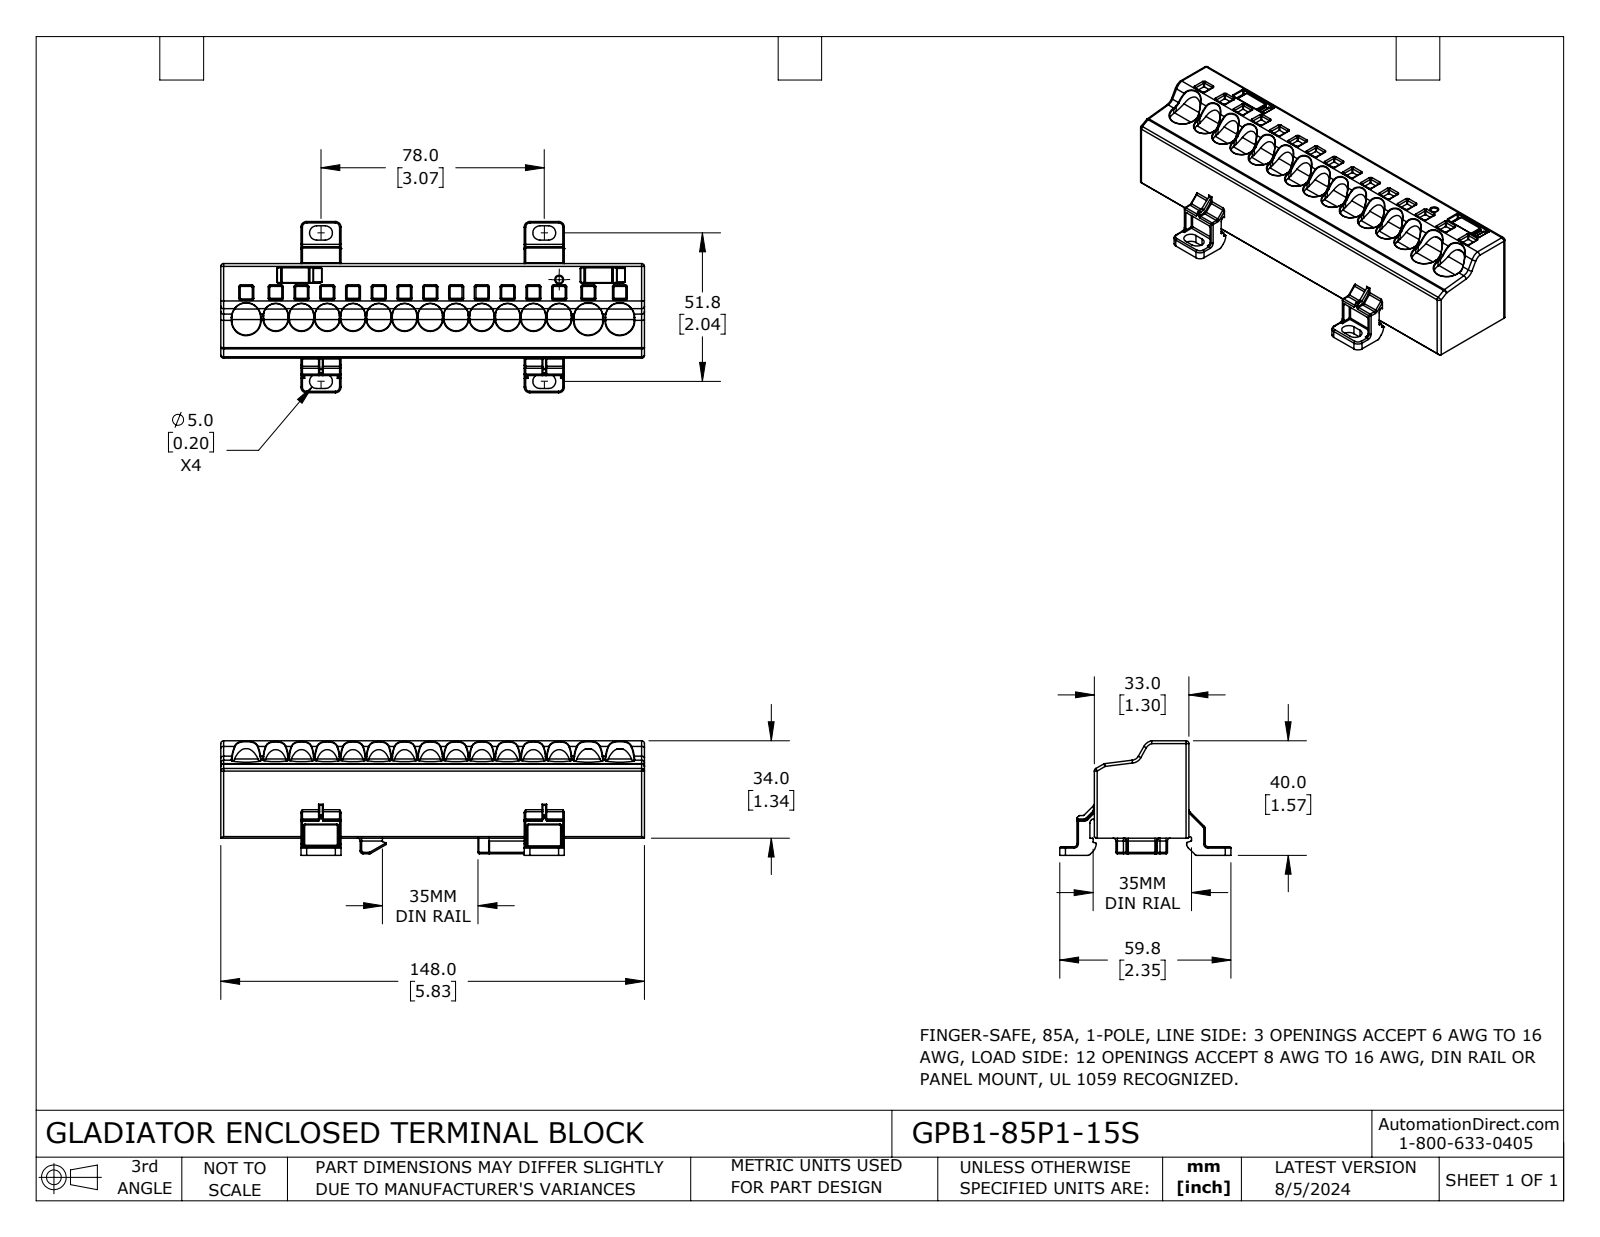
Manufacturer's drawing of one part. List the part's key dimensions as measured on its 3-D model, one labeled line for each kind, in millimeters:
Part name (STEP PRODUCT): GPB1-85P1-15S
STEP written by: SolidWorks 2023 (CONFIG_CONTROL_DESIGN)
Units: millimetres
Bodies: 1 solid, 1038 faces (292 planar, 426 cylindrical, 320 other)
Overall size (bounding box): 148 × 59.8 × 40
Volume: 150 400 mm³ · Surface area: 26 260 mm²
Round holes (diameter × count): ⌀2.5 ×1
Partial cylindrical surfaces — rounded edges, fillets, slot ends (radius × count): R0.5 ×92, R0.2 ×77, R0.3 ×35, R1 ×33, R4.2 ×24, R0.3 ×10, R2 ×10, R2.5 ×8
Main face-to-face distances: 33, 34, 148, 3, 6, 40, 2, 0.5, 39.5, 5.5
